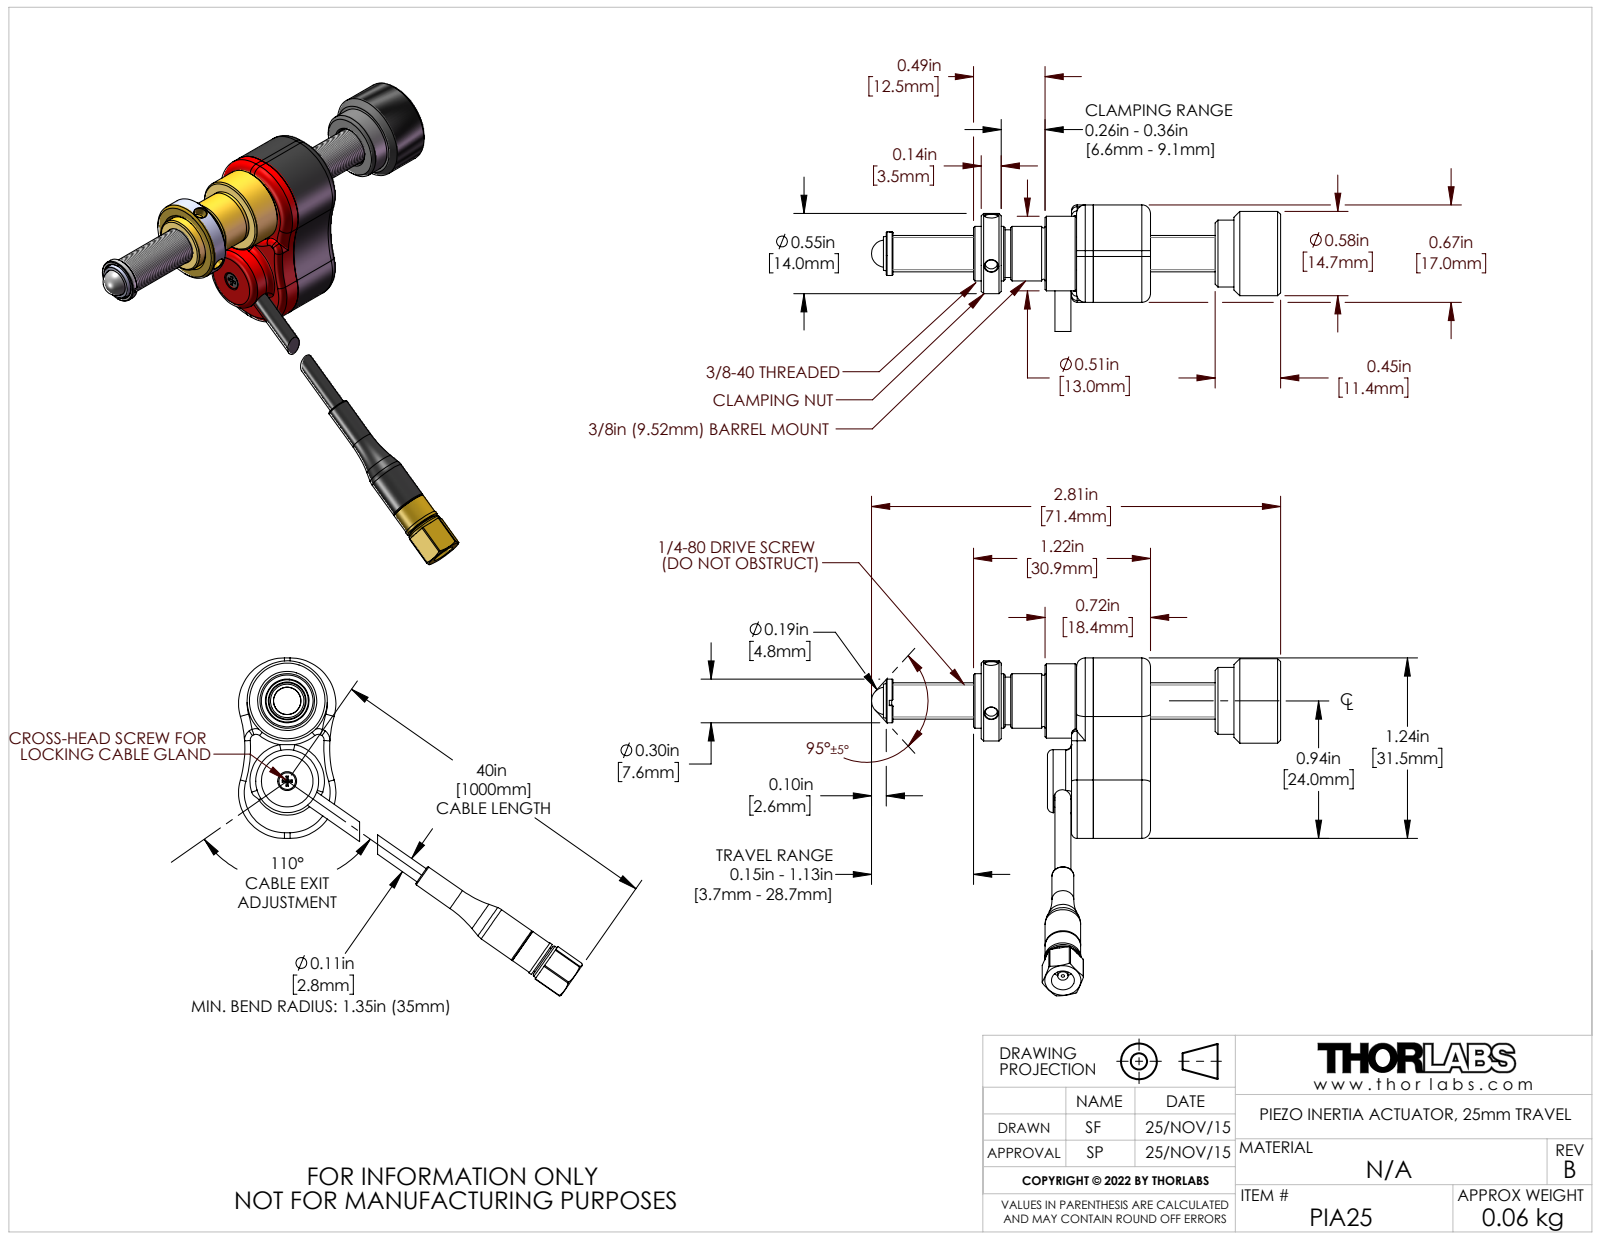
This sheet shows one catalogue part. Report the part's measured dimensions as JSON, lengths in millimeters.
{"part_name": "137518-9.5mm Barrel Mount; 137522 - 3_8-40 Retaining Nut; Copy of SMC Straight Plug_Crimp_R112075000_Farnell 4194305^169745-SMC Cable-1m; Copy of RG174 Strain Relief_Black_LEMO_GMD00028DN^169745-SMC Cable-1m (+8 more)", "step_written_by": "SolidWorks 2022 (CONFIG_CONTROL_DESIGN)", "units": "millimeters", "bodies": {"solids": 23, "faces": 1642, "planar": 683, "cylindrical": 392, "other": 567}, "overall_size": [71.42, 60.01, 58.98], "volume_mm3": 8257, "surface_area_mm2": 11685, "round_holes": [[1.25, 4], [2.2, 4], [1.8, 3], [0.9, 2], [0.47, 1], [0.57, 1], [0.8, 1], [1.6, 1], [2, 1], [2.03, 1], [2.8, 1], [3, 1]], "round_bosses_or_shafts": [[1.42, 6], [3, 4], [1.6, 2], [14.73, 1], [14, 1], [13, 1], [11.68, 1], [11, 1]], "partial_cylinders_radius": [[1, 18], [1.5, 6], [2, 6], [0.5, 4], [1.75, 4], [1.8, 4], [7, 4], [7.2, 4]], "face_to_face_distances": [9.1, 0.8, 2.5, 7.7, 1.1, 9.9, 0.7, 7.4, 12.1, 12.9], "hole_center_spacings": [5, 8.66, 19, 12.29, 1.34, 4.37, 4.65, 5.21]}
